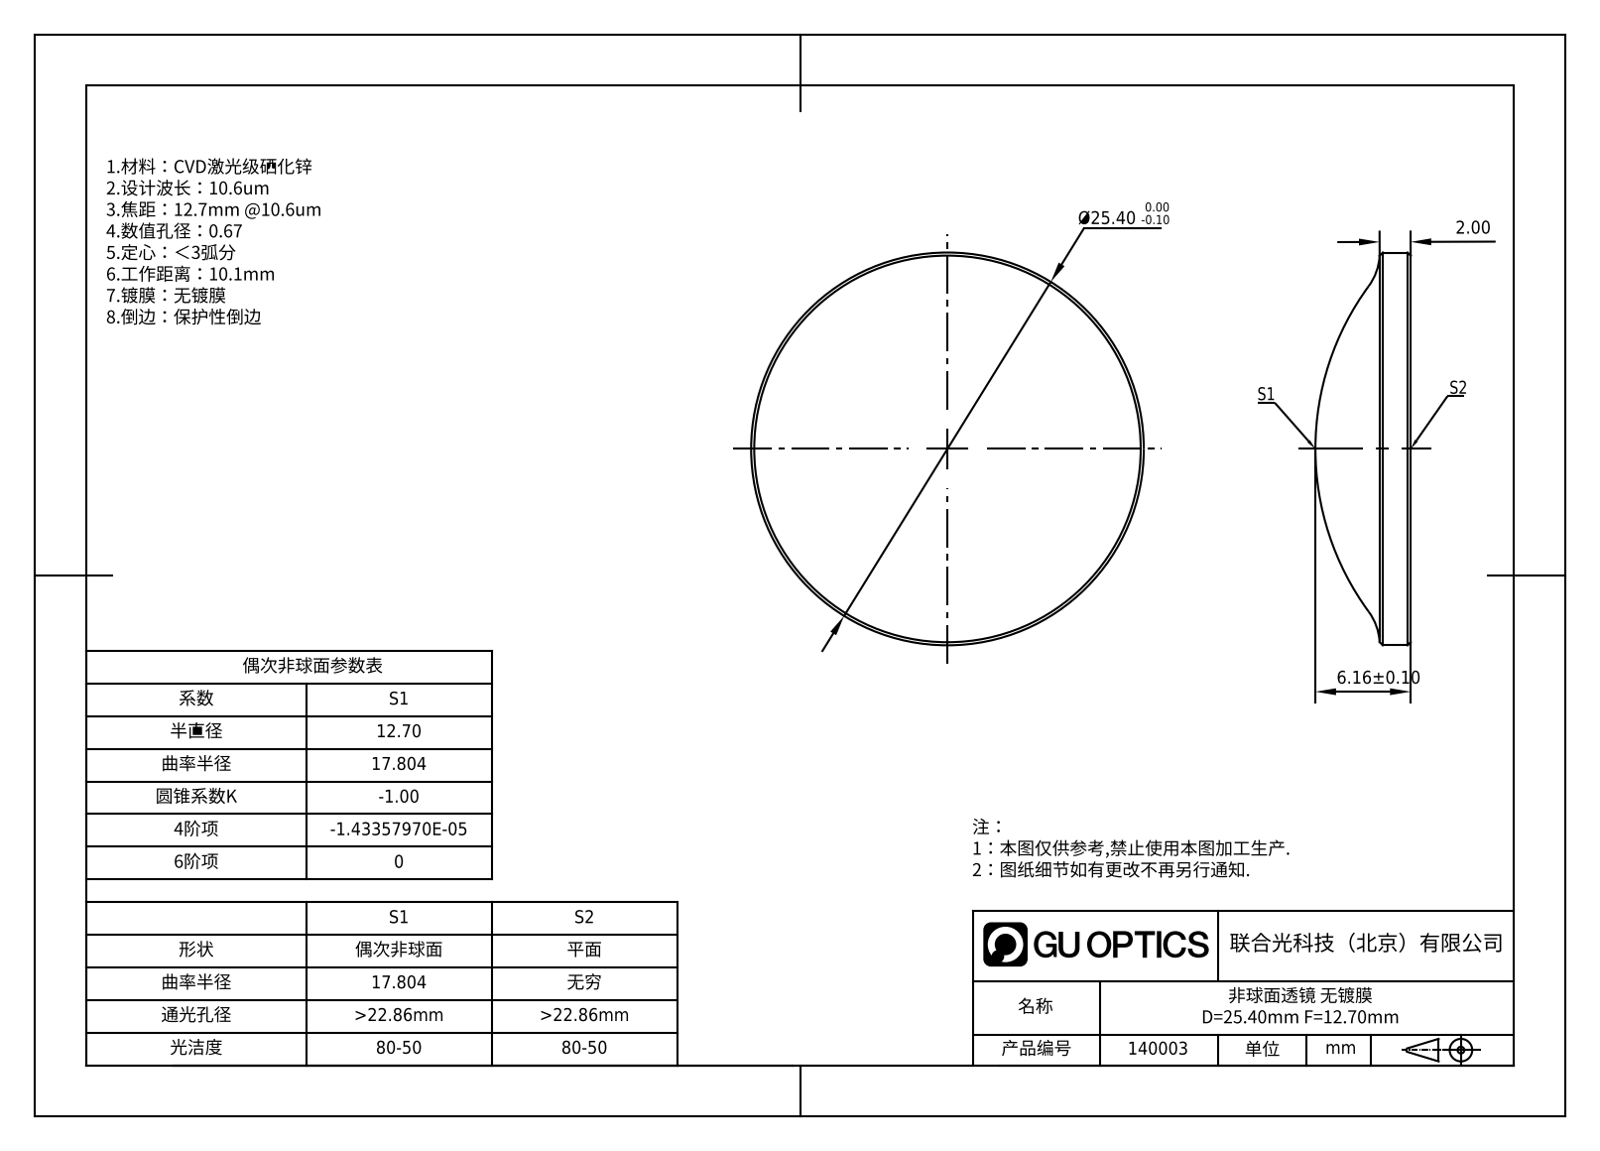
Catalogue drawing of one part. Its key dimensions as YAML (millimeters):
part_name: "140003"
step_written_by: "SolidWorks 2020 (CONFIG_CONTROL_DESIGN)"
units: millimeters
bodies: {solids: 1, faces: 5, planar: 1, cylindrical: 2, other: 2}
overall_size: [25.4, 25.4, 6.16]
volume: 2037
surface_area: 1222
round_bosses_or_shafts:
  - {diameter: 25.4, count: 1}
